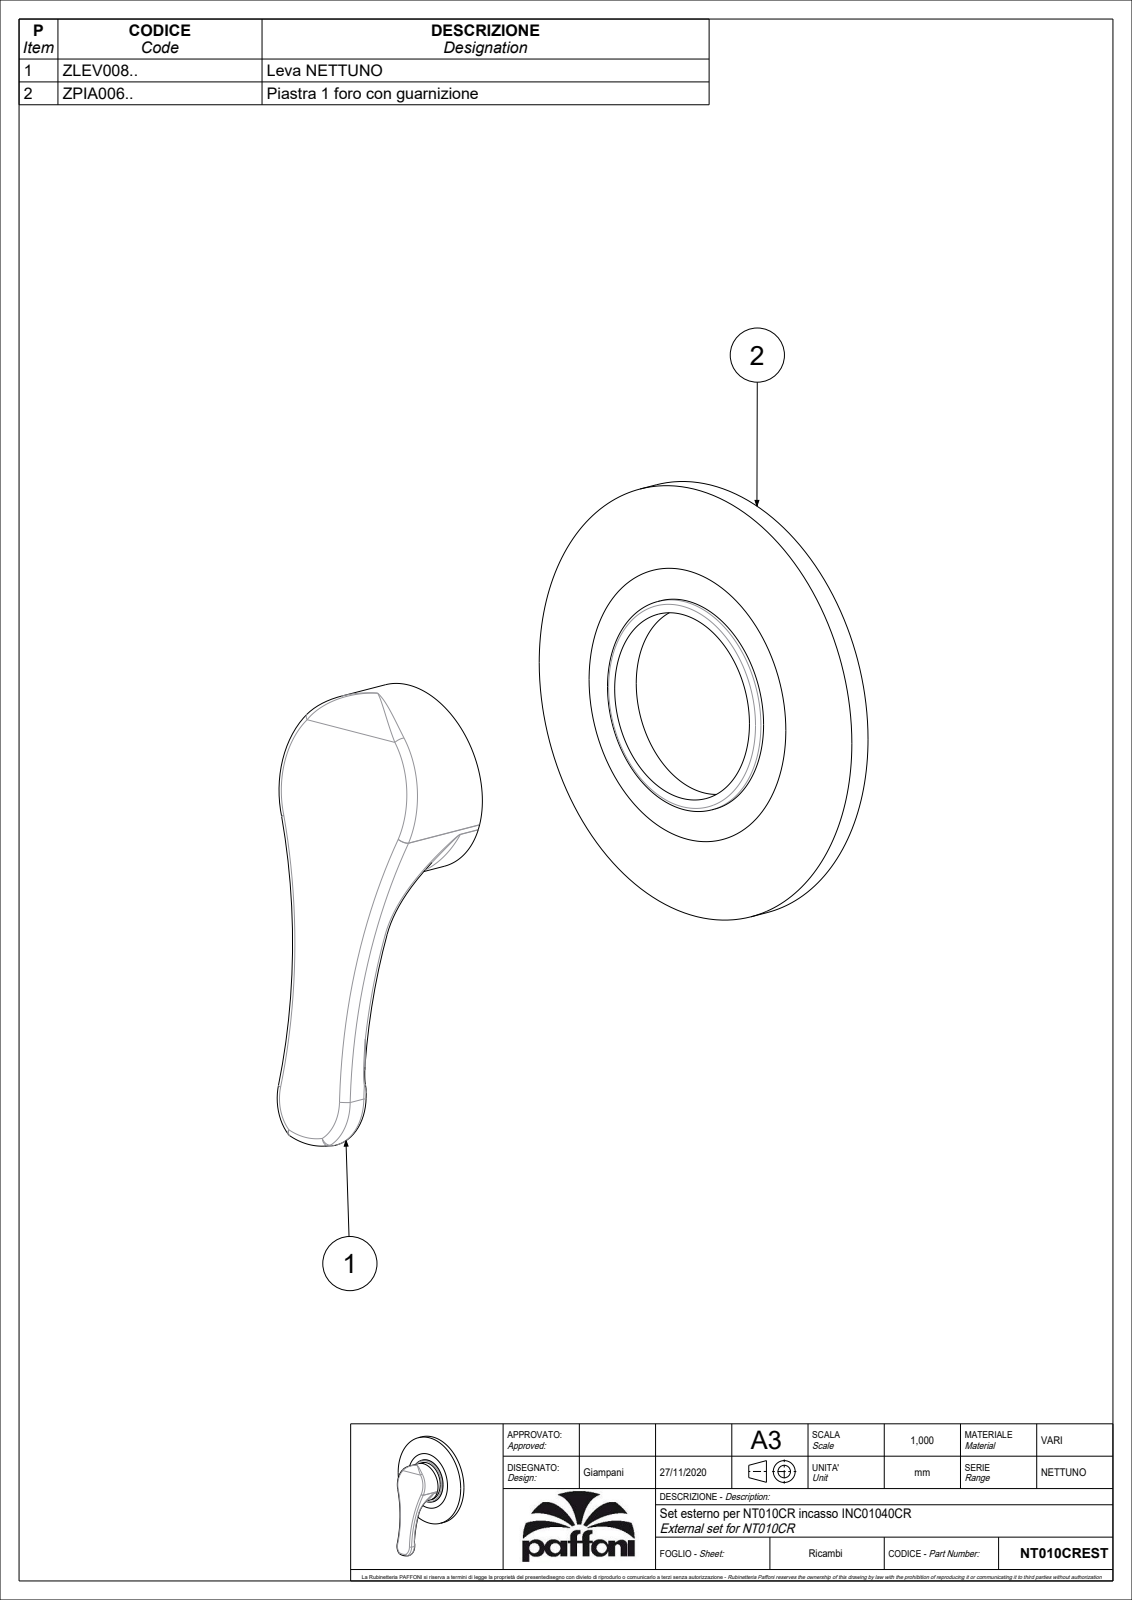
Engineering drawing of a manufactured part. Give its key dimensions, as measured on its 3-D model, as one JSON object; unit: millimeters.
{"part_name": "NT010CREST", "step_written_by": "CREO PARAMETRIC BY PTC INC, 2020044 (CONFIG_CONTROL_DESIGN)", "units": "millimeters", "bodies": {"solids": 2, "faces": 158, "planar": 47, "cylindrical": 50, "other": 61}, "overall_size": [151.71, 116, 55.84], "volume_mm3": 43661, "surface_area_mm2": 41418, "round_holes": [[4.5, 1], [6, 1], [9.4, 1], [47, 1], [50, 1], [115, 1]], "round_bosses_or_shafts": [[116, 1], [56.5, 1], [55, 1], [8, 1], [5, 1]], "partial_cylinders_radius": [[1, 5], [2, 4], [135, 2], [3.9, 1], [10, 1], [13, 1], [25, 1]], "face_to_face_distances": [7.96, 2.95, 5.01, 8, 2.45, 12.55, 3, 0.99, 3.94, 8.95]}
